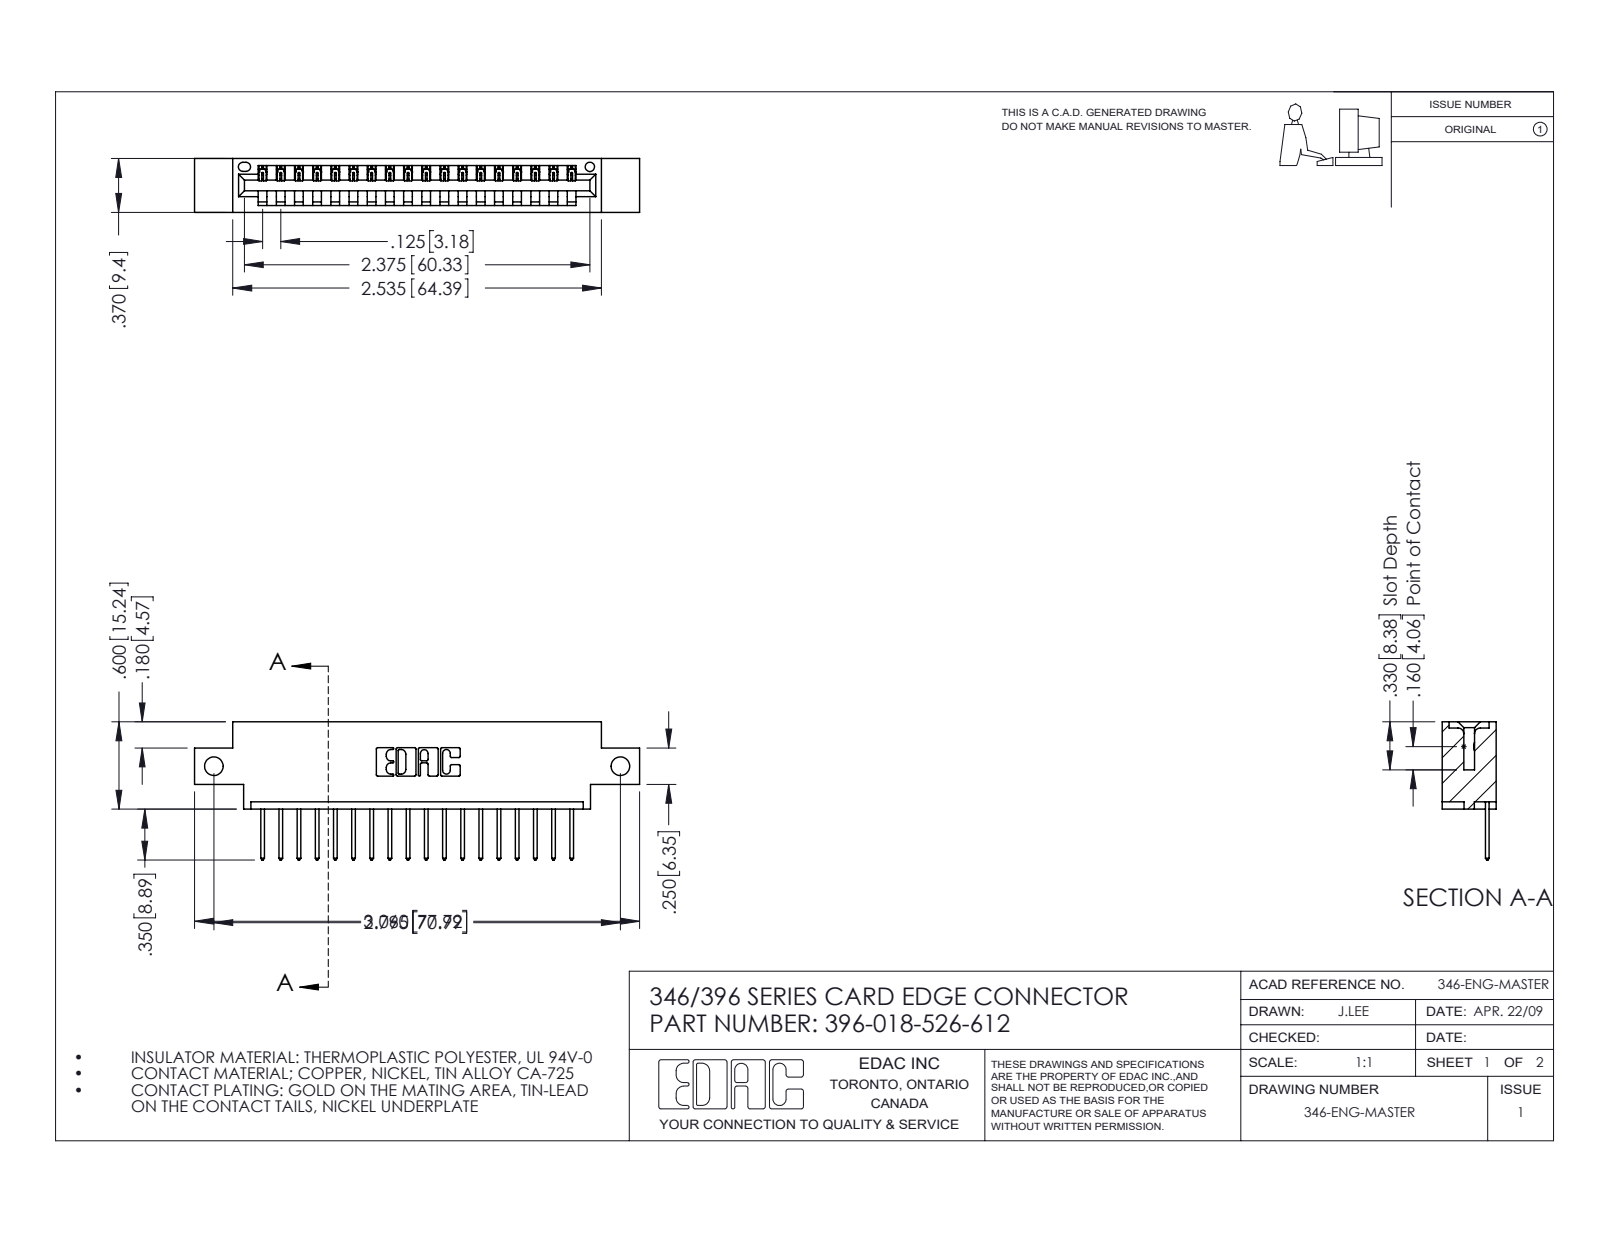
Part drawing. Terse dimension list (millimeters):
name: 396-018-526-612; 345-292-001_345-293-126; 346 Part_0.170 Offset - Side Mount
written by: SolidWorks 2016 (CONFIG_CONTROL_DESIGN)
unit: mm
bodies: 19 solids, 1170 faces (800 planar, 370 cylindrical, 0 other)
size: 77.7 × 24.1 × 9.4
volume: 7 010 mm³; area: 8 510 mm²
holes: 2× ⌀3.3, 1× ⌀1.6
rounds: 36× R0.2, 36× R0.3, 22× R0.3, 6× R0.2, 6× R0.8, 3× R0.7, 2× R0.8, 2× R1
face distances: 1.2, 8.2, 9.4, 6.4, 1.8, 7.6, 0.6, 3.8, 5.6, 2.5
hole spacings: 71
